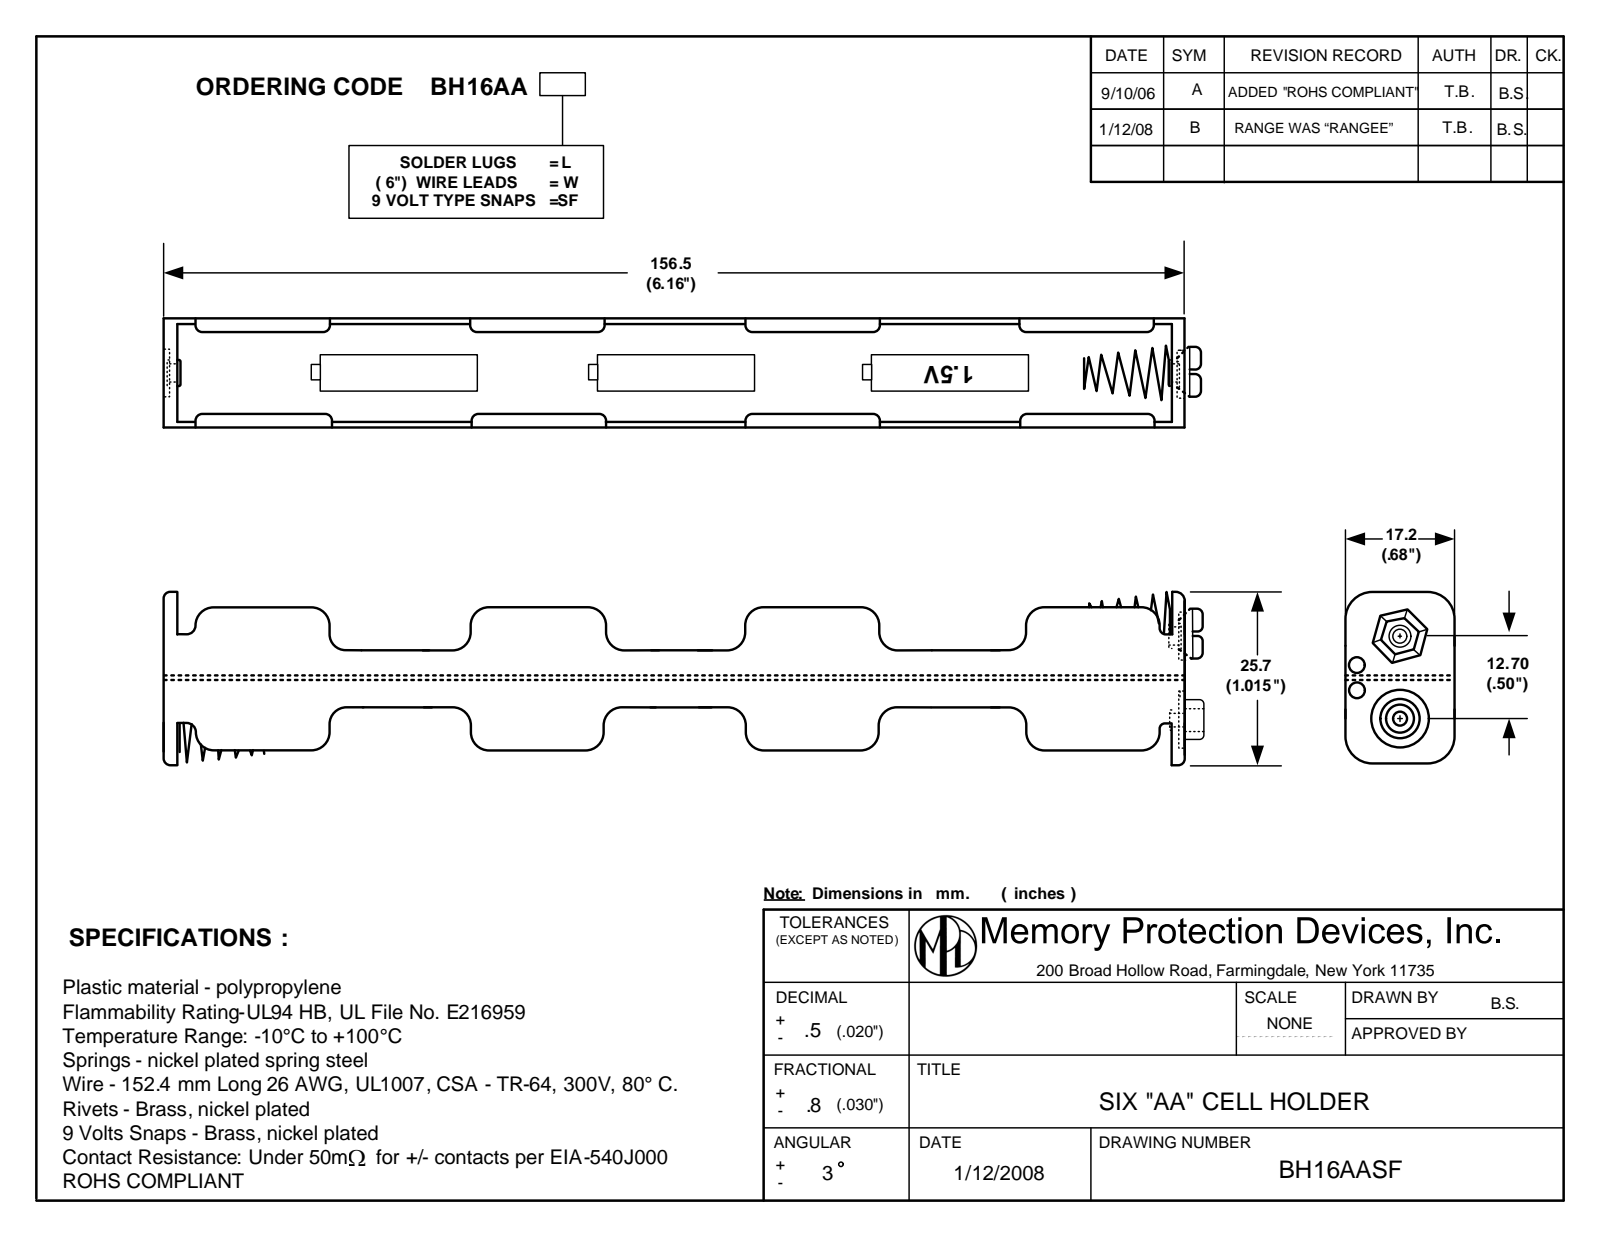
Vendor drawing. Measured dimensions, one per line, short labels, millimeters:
name: BH16AASF
written by: SolidWorks 2017 (AUTOMOTIVE_DESIGN)
unit: mm
bodies: 5 solids, 757 faces (257 planar, 312 cylindrical, 188 other)
size: 159.94 × 25.7 × 17.2
volume: 11 015 mm³; area: 19 518 mm²
holes: 2× ⌀1.6, 2× ⌀2.3, 2× ⌀2.54, 2× ⌀9.5, 1× ⌀4.95
bosses: 2× ⌀9.14, 2× ⌀7, 2× ⌀6.2, 2× ⌀3.8, 2× ⌀0.63, 1× ⌀7.92, 1× ⌀5.71
rounds: 52× R0.25, 32× R1.91, 12× R0.38, 6× R0.76, 6× R0.89, 4× R2.5, 4× R6.17, 4× R9.5
face distances: 1.3, 15.9, 17.2, 14.6, 155.16, 153.86, 0.31, 156.15, 0.99, 154.85
hole spacings: 7.48, 10.23, 3.84, 12.7
